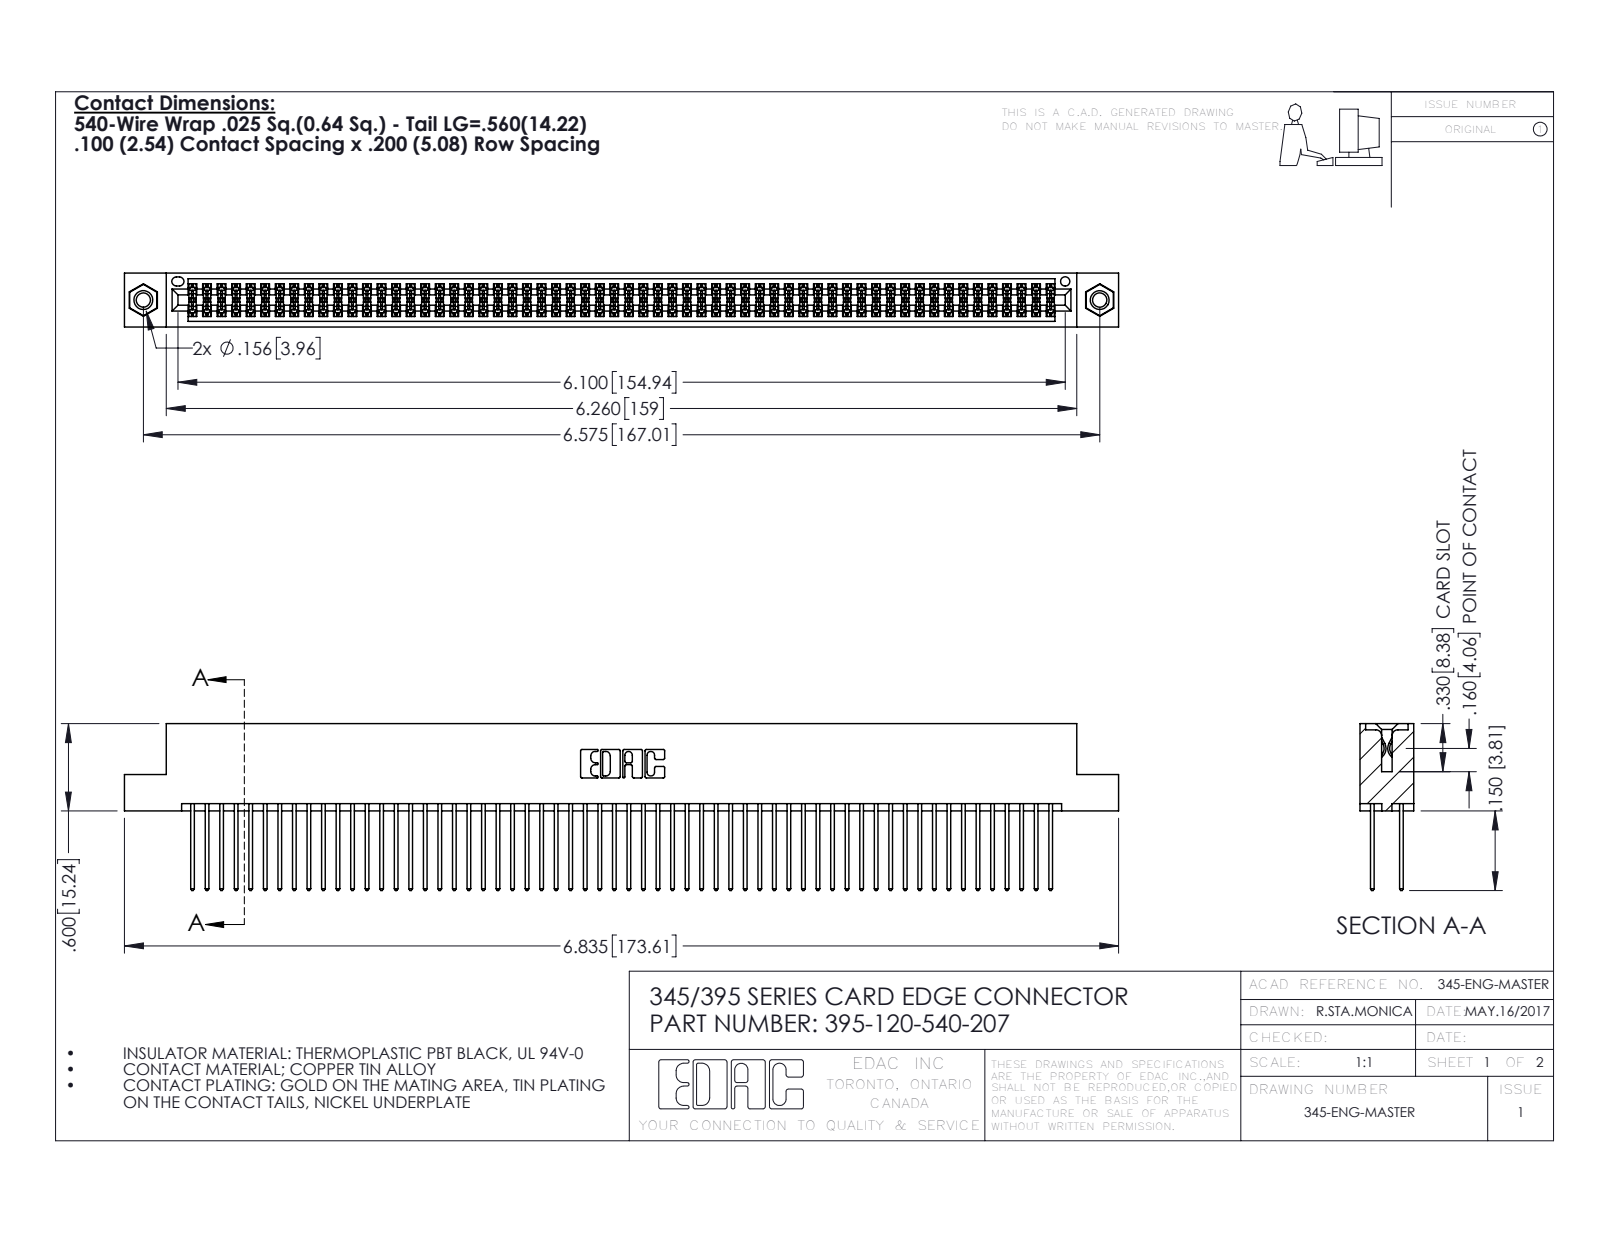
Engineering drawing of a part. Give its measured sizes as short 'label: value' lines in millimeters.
name: 345 Part_Flush Mounting Lugs - 0.156 Dia-TI; 345-292-001_345-293-140; 345-250-001_345-250-005-103; 395-120-540-207
written by: SolidWorks 2016 (CONFIG_CONTROL_DESIGN)
unit: mm
bodies: 123 solids, 6186 faces (4072 planar, 2098 cylindrical, 16 other)
size: 173.6 × 29.1 × 9.4
volume: 17 470 mm³; area: 28 320 mm²
holes: 2× ⌀2.5, 2× ⌀3.2, 2× ⌀4, 1× ⌀1.6
bosses: 2× ⌀3.9
rounds: 180× R0.2, 120× R0.3, 22× R0.3, 6× R0.2, 6× R0.8, 3× R0.7, 2× R0.4, 2× R0.5
face distances: 1.8, 7.6, 5.1, 2.5, 6.9, 0.6, 9.4, 5.7, 4.4, 3.8
hole spacings: 6.9, 161, 167
